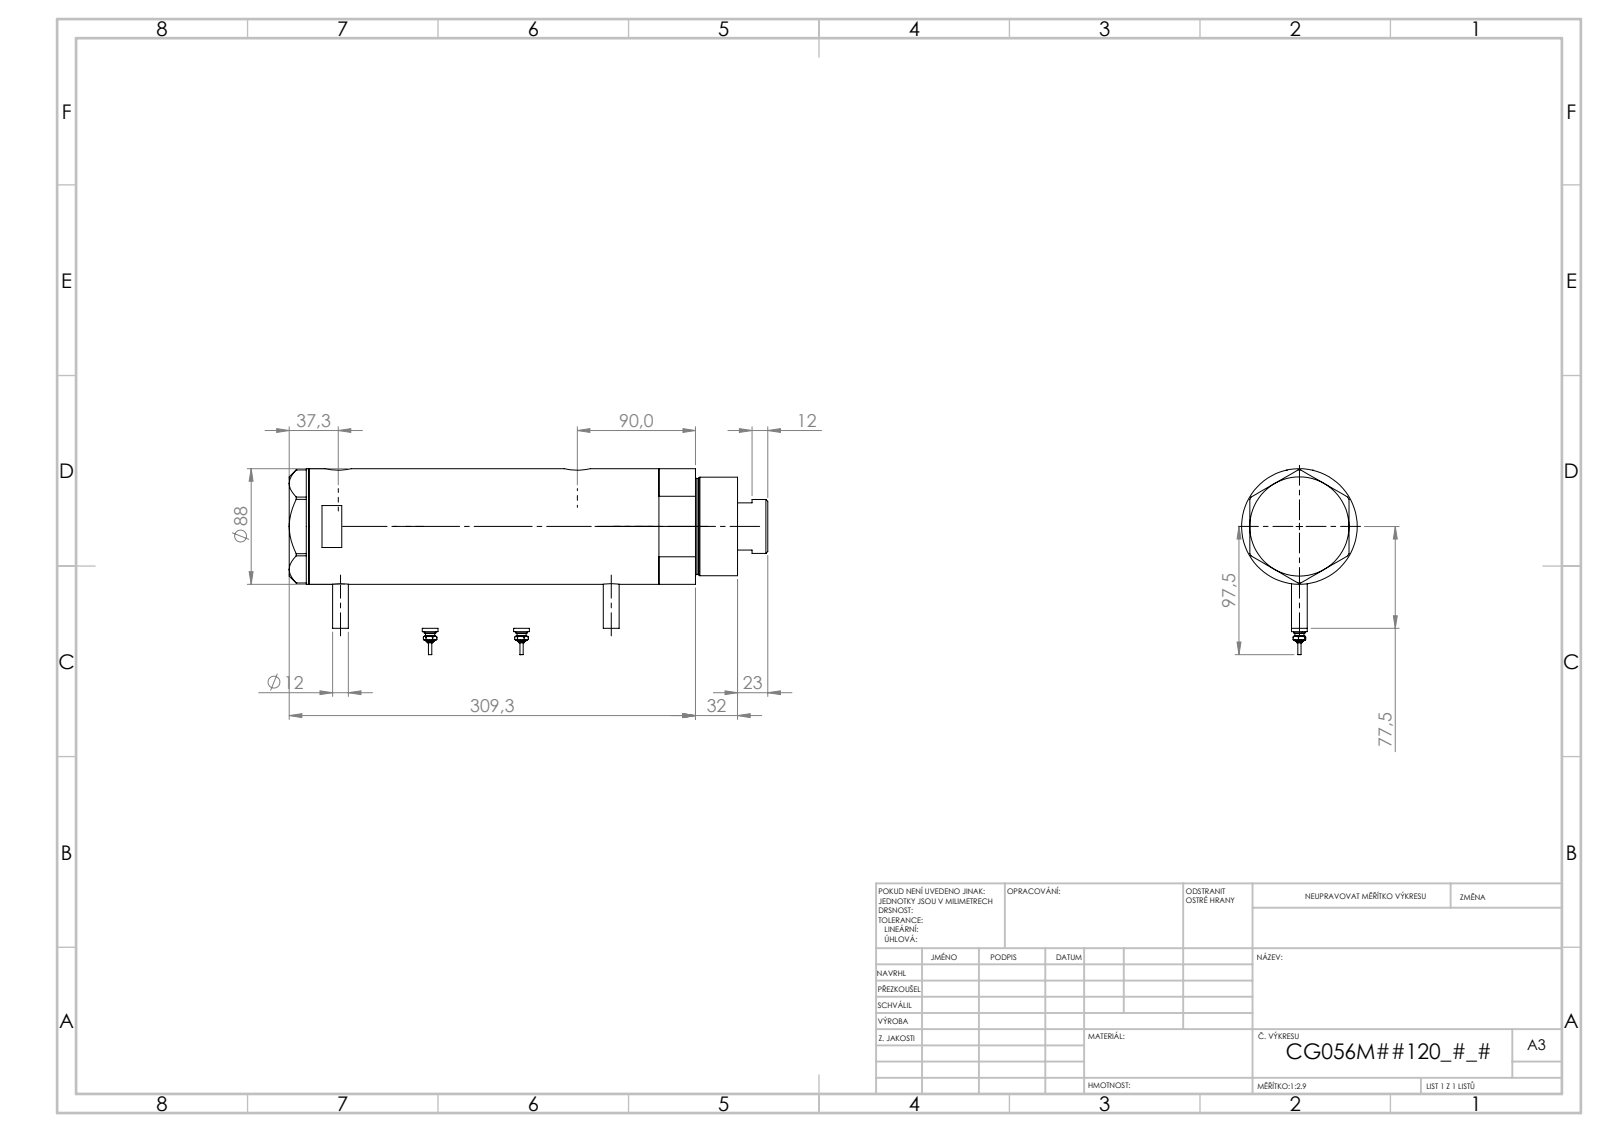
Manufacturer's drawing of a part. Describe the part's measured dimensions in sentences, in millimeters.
The part is named "V270CG_MIDDLE; V270CG_VC; V270CG_BACK; V270CG_FRONT (+1 more)". Its 3-D file was written by "SolidWorks 2019 (CONFIG_CONTROL_DESIGN)". It is 6 solids with 232 faces: 81 planar, 77 cylindrical and 74 other. Overall it measures 344.47 by 120.3 by 88 millimeters. Its volume is 1 765 000 cubic millimeters and its surface area 252 327 square millimeters. Round holes: 2 of diameter 5, 2 of diameter 12.5, 2 of diameter 13.16, 2 of diameter 20, 1 of diameter 14.5, 1 of diameter 42, 1 of diameter 43.5, 1 of diameter 56, 1 of diameter 60, 1 of diameter 80. Round bosses or shafts: 2 of diameter 12, 2 of diameter 9, 2 of diameter 7, 2 of diameter 4.34, 2 of diameter 2.4, 1 of diameter 88, 1 of diameter 75, 1 of diameter 73. The main face-to-face distances are 194.4, 26, 168.4, 15, 41, 209.4, 306.47, 321.47, 280.47, 112.07. The hole center spacings are 1.7, 25.8, 170.3, 172, 196.1, 197.8.
